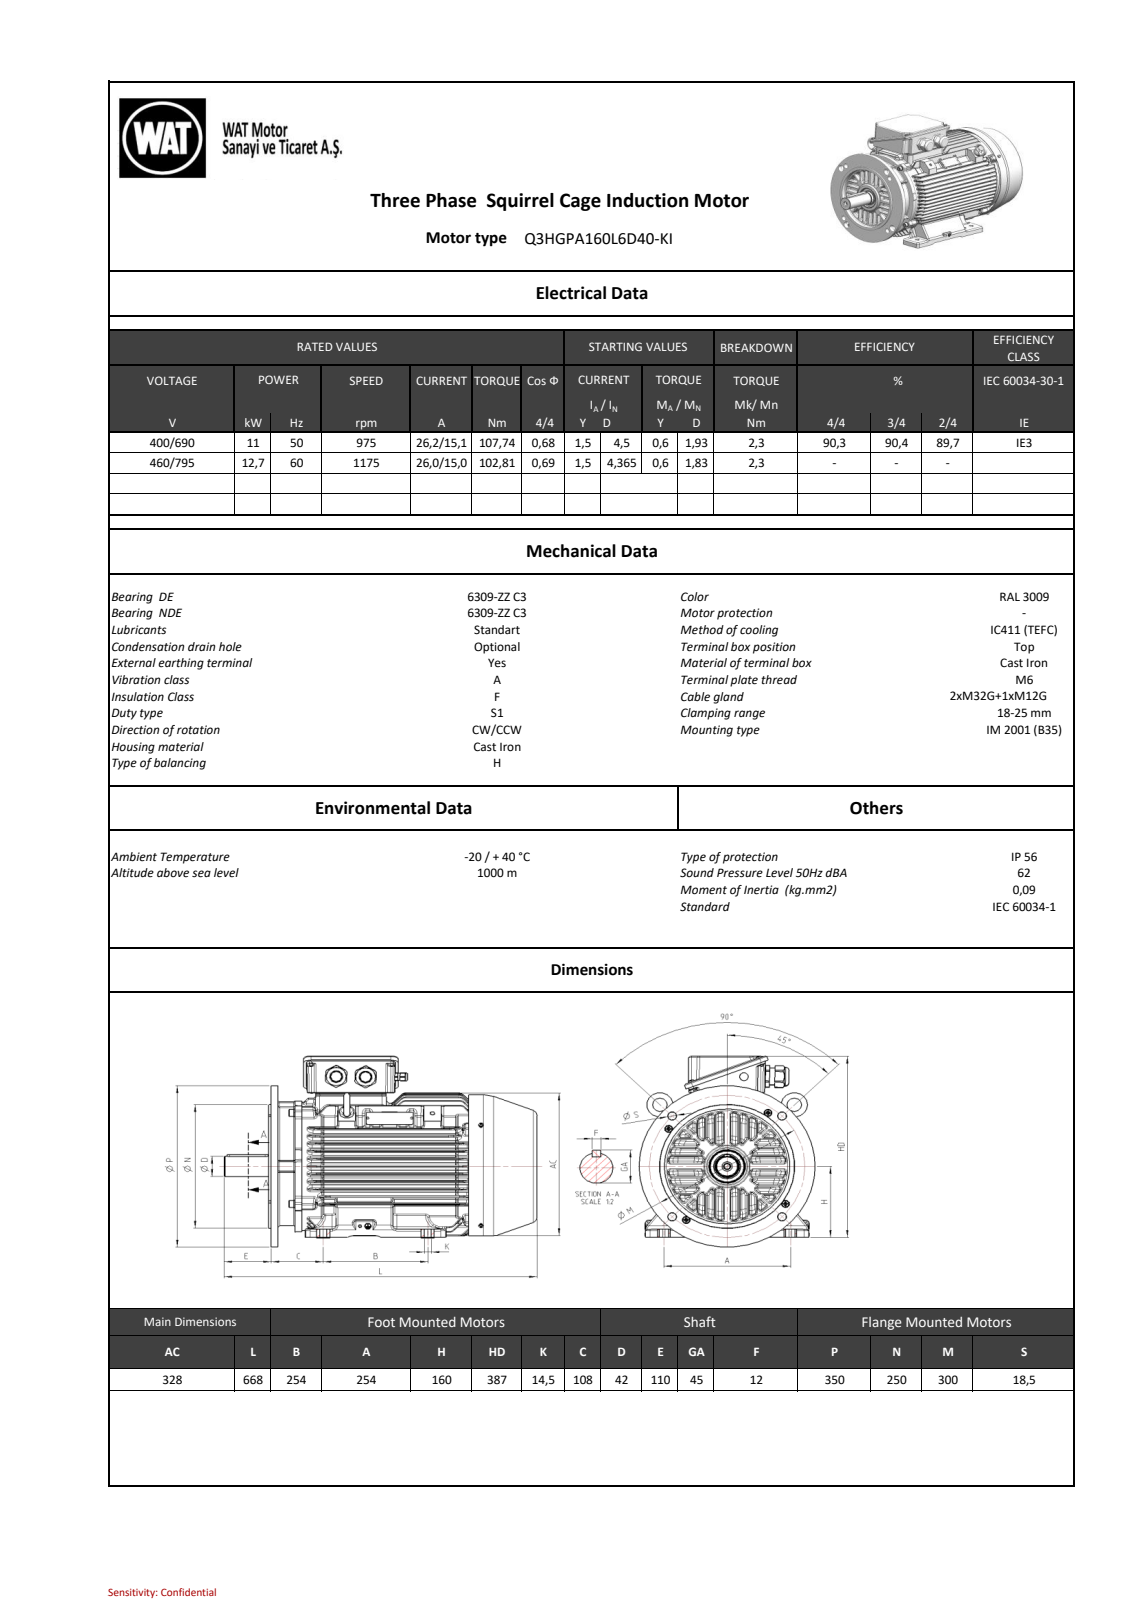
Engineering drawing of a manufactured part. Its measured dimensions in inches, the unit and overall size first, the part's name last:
Units: inches
Overall size (bounding box): 26.28 × 15.843 × 13.78
Round holes (diameter × count): ⌀0.354 ×8, ⌀0.165 ×7, ⌀0.217 ×6, ⌀0.209 ×4, ⌀0.728 ×4, ⌀0.906 ×4, ⌀0.429 ×2, ⌀0.098 ×1, ⌀0.205 ×1, ⌀0.394 ×1, ⌀0.551 ×1, ⌀0.669 ×1
Round bosses / shafts (diameter × count): ⌀0.63 ×8, ⌀0.787 ×4, ⌀0.394 ×4, ⌀1.181 ×2, ⌀13.78 ×1, ⌀12.48 ×1, ⌀11.102 ×1, ⌀10.079 ×1
Partial cylindrical surfaces — rounded edges, fillets, slot ends (radius × count): R0.197 ×244, R0.118 ×199, R0.157 ×139, R0.059 ×112, R0.079 ×80, R0.071 ×58, R0.236 ×31, R0.016 ×30
Main face-to-face distances: 5.411, 0.597, 1.198, 4.811, 0.6, 1.8, 4.208, 1.203, 0.603, 4.214
Hole centre spacings: 5.354, 1.036, 5.669, 7.443, 8.018, 8.869, 11.531, 1.969
Bodies: 0 solids, 6608 faces (1218 planar, 1884 cylindrical, 3506 other)
Part name (STEP PRODUCT): 26000C948E142t15
STEP written by: SIEMENS PLM Software NX 11.0 (AUTOMOTIVE_DESIGN)
